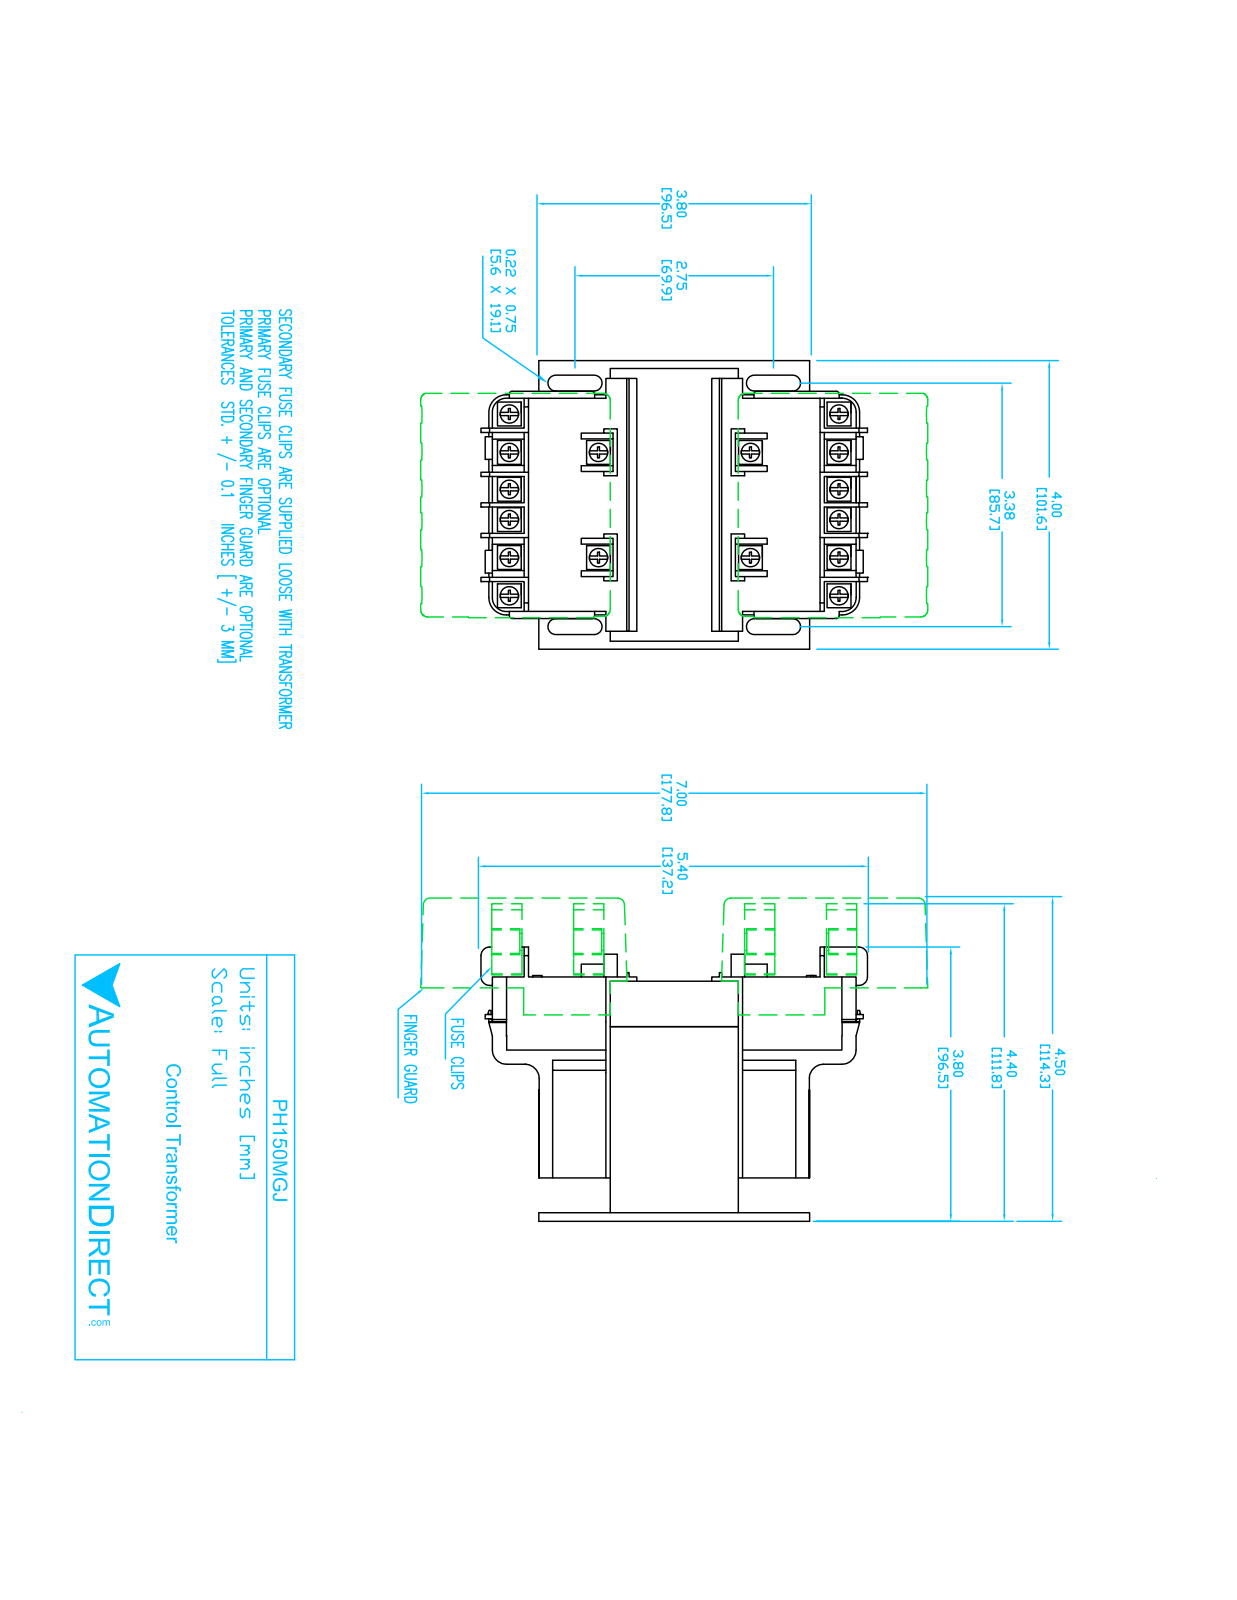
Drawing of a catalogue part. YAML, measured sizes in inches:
part_name: "PH150MGJ"
step_written_by: "SolidWorks 2017 (AUTOMOTIVE_DESIGN)"
units: inches
bodies: {solids: 8, faces: 596, planar: 380, cylindrical: 154, other: 62}
overall_size: [5.35, 4, 3.74]
volume: 46.36
surface_area: 180.7
round_holes:
  - {diameter: 0.157, count: 4}
partial_cylinders:
  - {radius: 0.039, count: 58}
  - {radius: 0.197, count: 16}
  - {radius: 0.11, count: 8}
  - {radius: 0.125, count: 4}
  - {radius: 0.188, count: 4}
  - {radius: 0.243, count: 4}
  - {radius: 0.472, count: 2}
face_to_face_distances: [1.772, 0.069, 1.033, 1.102, 2.52, 2.589, 3.622, 0.63, 0.472, 3.15]
hole_center_spacings: [0.787, 3.375, 3.465]
